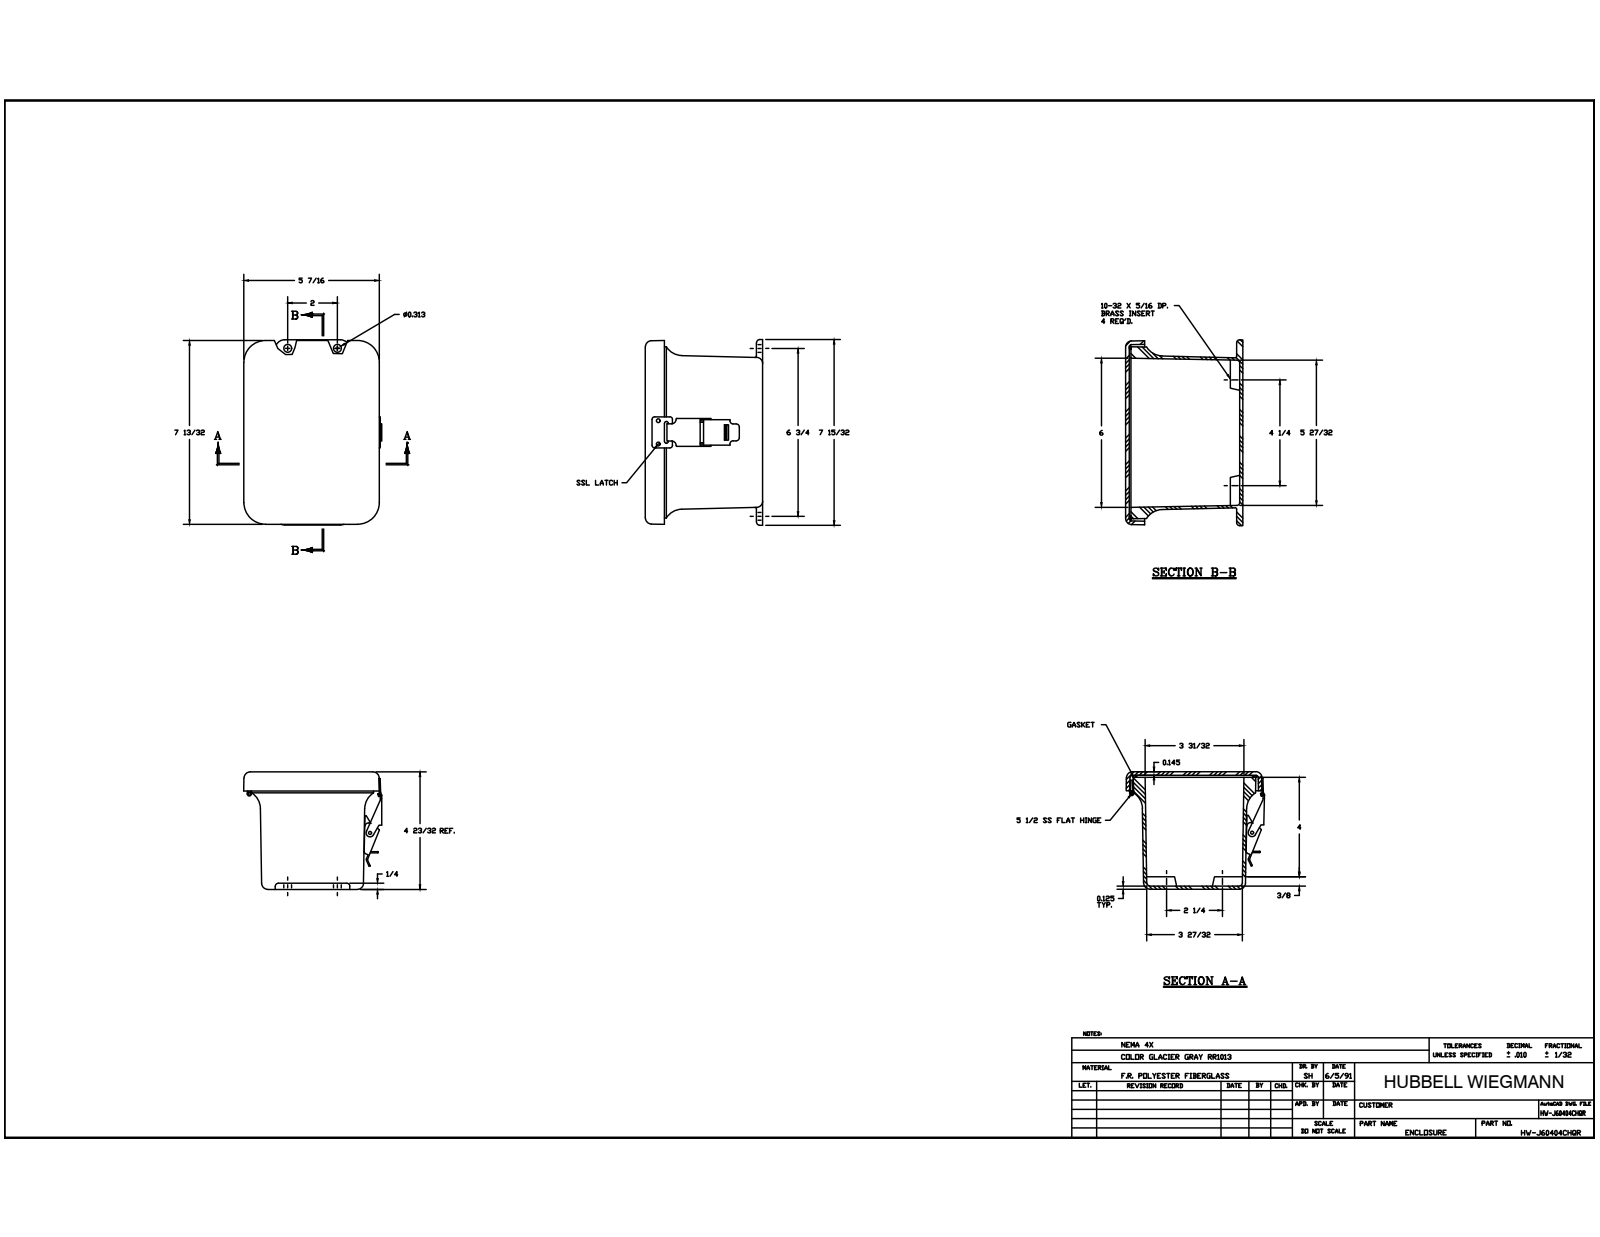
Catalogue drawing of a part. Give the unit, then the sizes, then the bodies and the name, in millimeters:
Units: millimetres
Overall size (bounding box): 189.85 × 142.68 × 119.82
Round holes (diameter × count): ⌀3.56 ×11, ⌀3.33 ×5, ⌀3.86 ×5, ⌀2.64 ×4, ⌀3.96 ×4, ⌀5.54 ×4, ⌀3.3 ×2, ⌀3.43 ×2, ⌀2.16 ×1, ⌀9.52 ×1
Round bosses / shafts (diameter × count): ⌀3.17 ×9, ⌀6.35 ×5, ⌀6.86 ×4, ⌀7.62 ×1, ⌀4.31 ×1, ⌀3.94 ×1, ⌀3.05 ×1
Partial cylindrical surfaces — rounded edges, fillets, slot ends (radius × count): R0.79 ×20, R3.17 ×16, R0.38 ×12, R1.14 ×8, R6.35 ×8, R0.76 ×6, R0.57 ×5, R5.08 ×5
Main face-to-face distances: 3.68, 116.14, 119.82, 3.18, 112.96, 116.64, 114.3, 111.12, 1.84, 5.52
Hole centre spacings: 23.81, 63.5, 84.81, 19.05, 11.92, 12.7, 34.07, 37.25
Volume: 517 872 mm³ · Surface area: 263 086 mm²
Bodies: 25 solids, 627 faces (249 planar, 254 cylindrical, 124 other)
Part name (STEP PRODUCT): J604HL_2; RMINS45821P_19; RMINS45821P_20; RMINS45821P_21 (+8 more)
STEP written by: Autodesk Inventor 2014 (AUTOMOTIVE_DESIGN)
